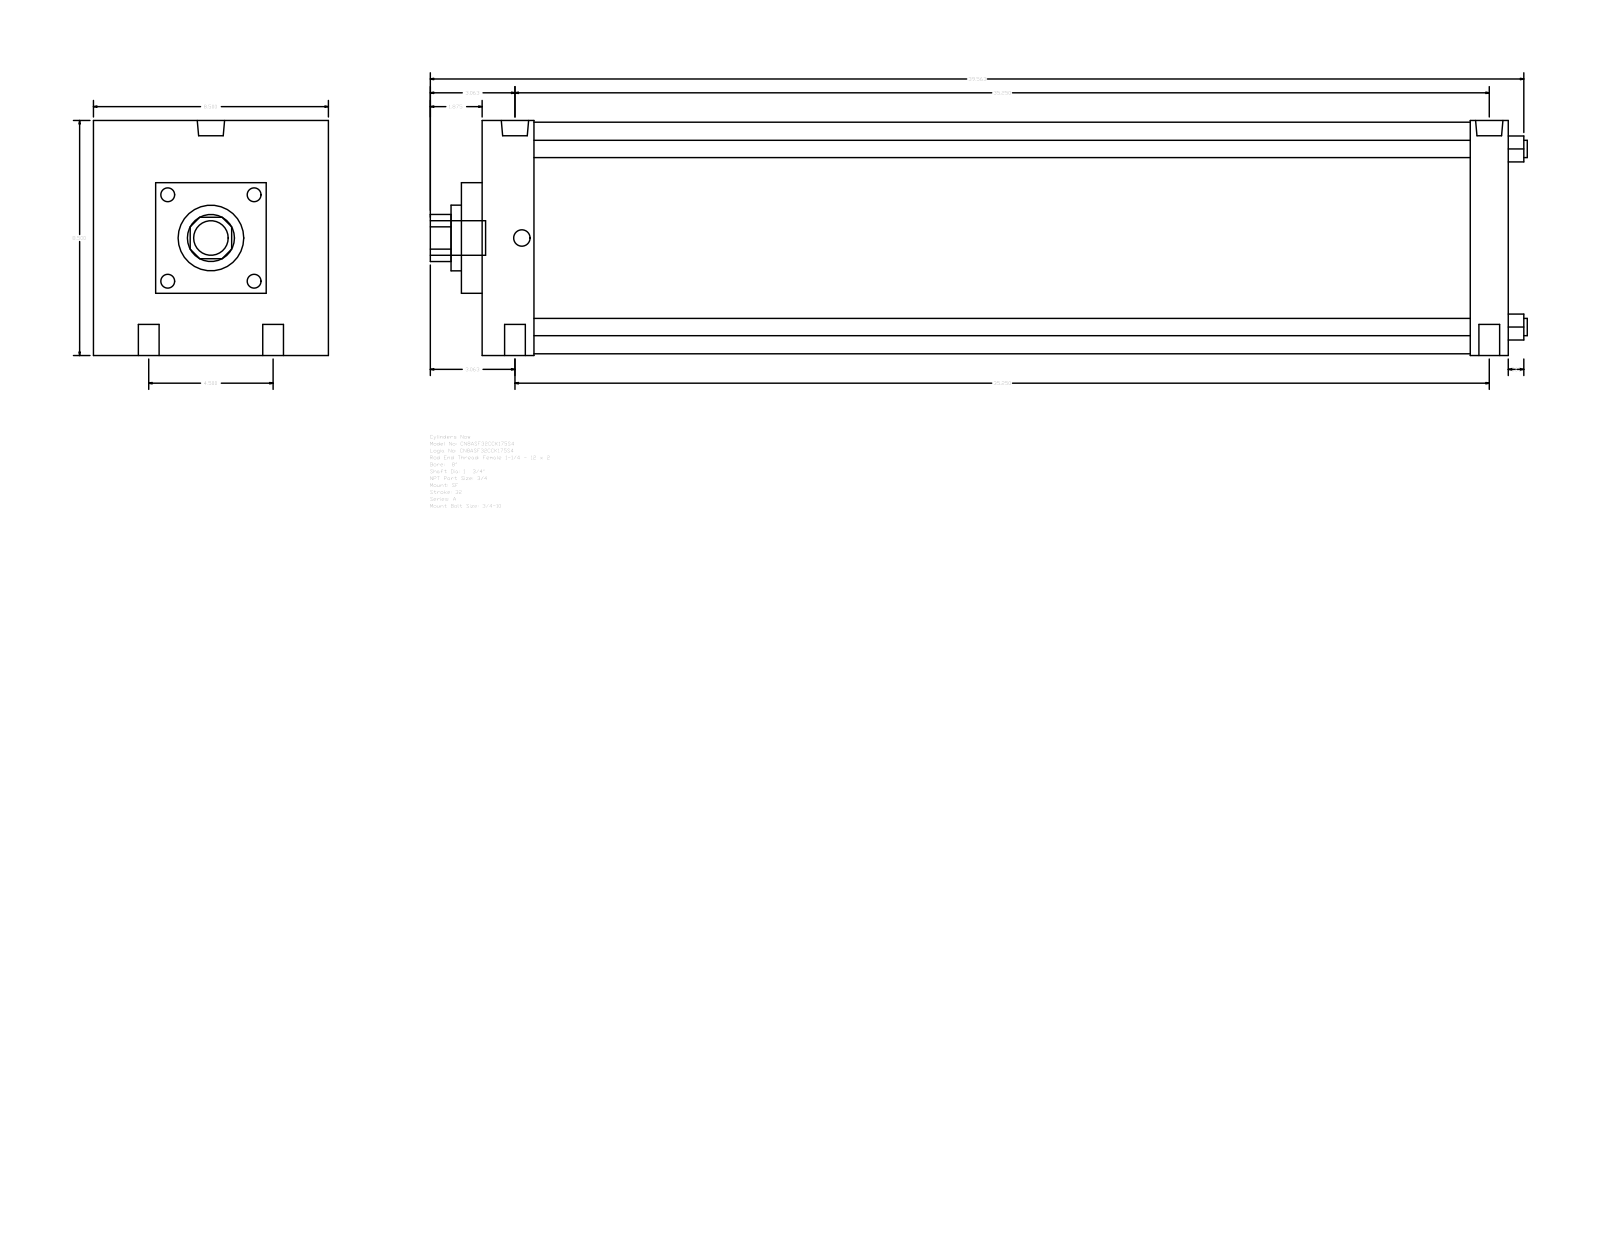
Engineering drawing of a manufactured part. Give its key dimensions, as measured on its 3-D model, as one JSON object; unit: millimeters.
{"part_name": "A_SF__0800_1.75", "step_written_by": "GSSL Pune (CONFIG_CONTROL_DESIGN)", "units": "millimeters", "bodies": {"solids": 0, "faces": 93, "planar": 67, "cylindrical": 26, "other": 0}, "overall_size": [1008.06, 215.9, 215.9], "round_holes": [[19.05, 4], [15.08, 2], [25.12, 2], [44.45, 1], [60.33, 1]], "round_bosses_or_shafts": [[15.88, 4], [212.72, 1], [31.75, 1]], "partial_cylinders_radius": [[21.63, 1]], "face_to_face_distances": [942.98, 215.9, 47.63, 908.05, 860.42, 895.35, 34.93, 19.05, 158.75, 57.15], "hole_center_spacings": [57.15, 897.17, 895.35, 114.3, 902.62, 882.65]}
